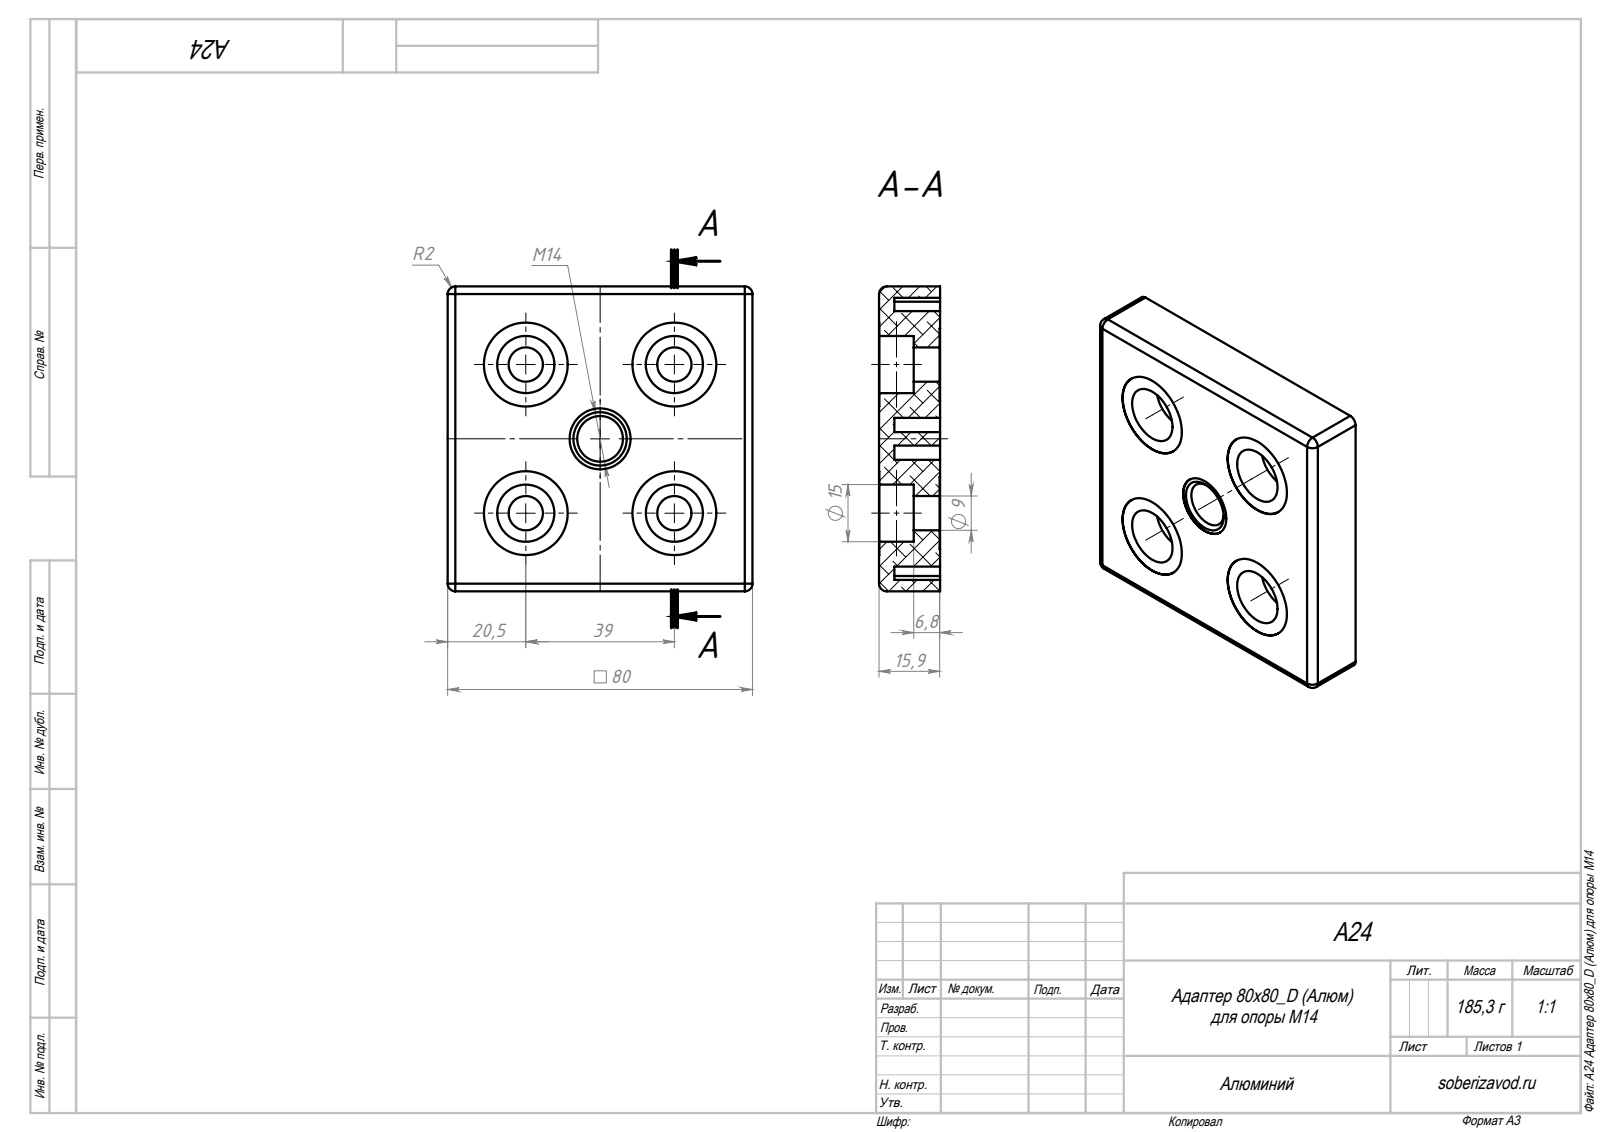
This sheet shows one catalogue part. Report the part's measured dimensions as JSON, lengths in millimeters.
{"step_written_by": "SolidWorks 2018 (AUTOMOTIVE_DESIGN)", "units": "millimeters", "bodies": {"solids": 1, "faces": 220, "planar": 72, "cylindrical": 140, "other": 8}, "overall_size": [80, 80, 16], "volume_mm3": 70708, "surface_area_mm2": 29492, "round_holes": [[5, 6], [9, 4], [15, 4], [19, 4], [22, 4], [12, 1], [16, 1]], "round_bosses_or_shafts": [[5, 6]], "partial_cylinders_radius": [[1, 24], [2, 8], [14, 4], [18.5, 1]], "face_to_face_distances": [16, 77, 3, 80, 12, 4, 74, 38.25, 41.75, 35.25], "hole_center_spacings": [31.32, 12.73, 14.85, 19.98, 21, 21.08, 27.58, 39]}
